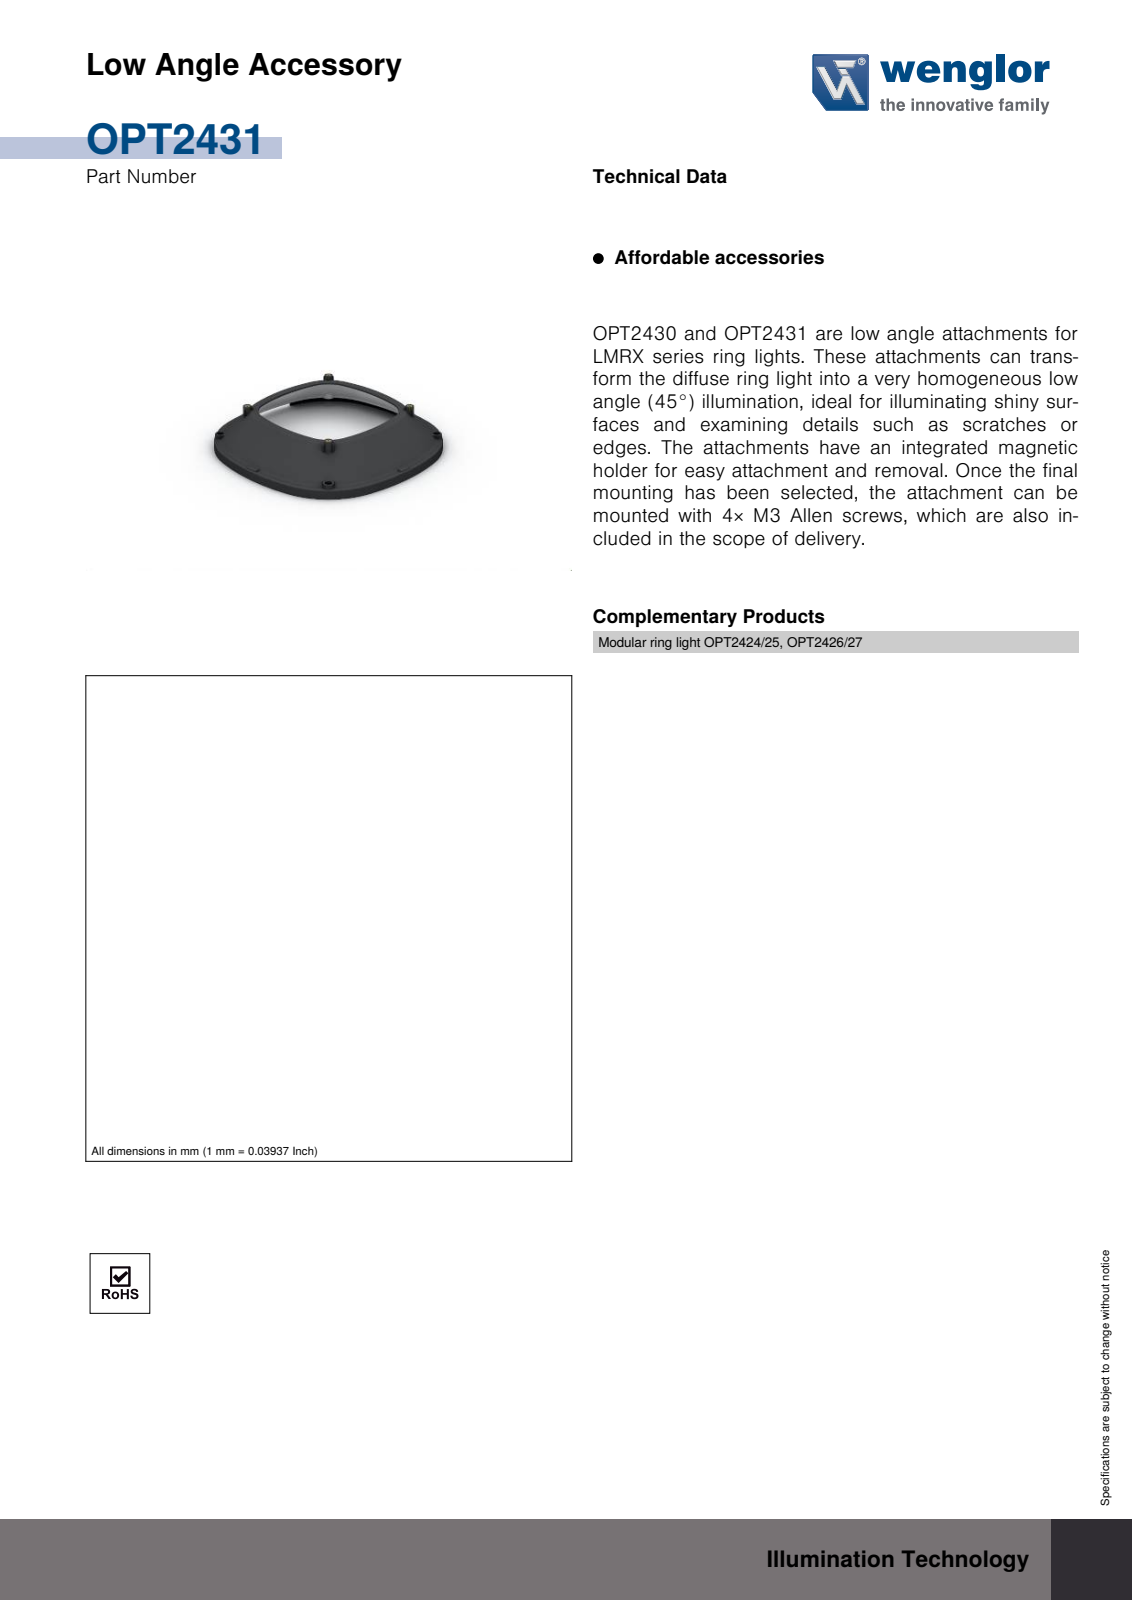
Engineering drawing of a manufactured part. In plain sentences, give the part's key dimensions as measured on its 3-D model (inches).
The part is named "OPT2431". Its 3-D file was written by "SolidWorks 2021 (AUTOMOTIVE_DESIGN)". It is 1 solid with 905 faces: 144 planar, 159 cylindrical and 602 other. Overall it measures 7.755 by 7.696 by 1.624 inches. Its volume is 4.021 cubic inches and its surface area 104 square inches. Round holes: 4 of diameter 0.118, 4 of diameter 0.167. Partial cylindrical surfaces (rounded edges, fillets, slot ends): 96 of radius 0.01, 11 of radius 0.059, 5 of radius 0.02, 4 of radius 0.262, 4 of radius 1.004, 3 of radius 5.811, 1 of radius 5.811. The main face-to-face distances are 0.098, 0.266, 0.364, 0.157, 0.079, 0.177, 0.423, 0.059, 0.522, 0.256. The hole center spacings are 4.173, 5.902.
